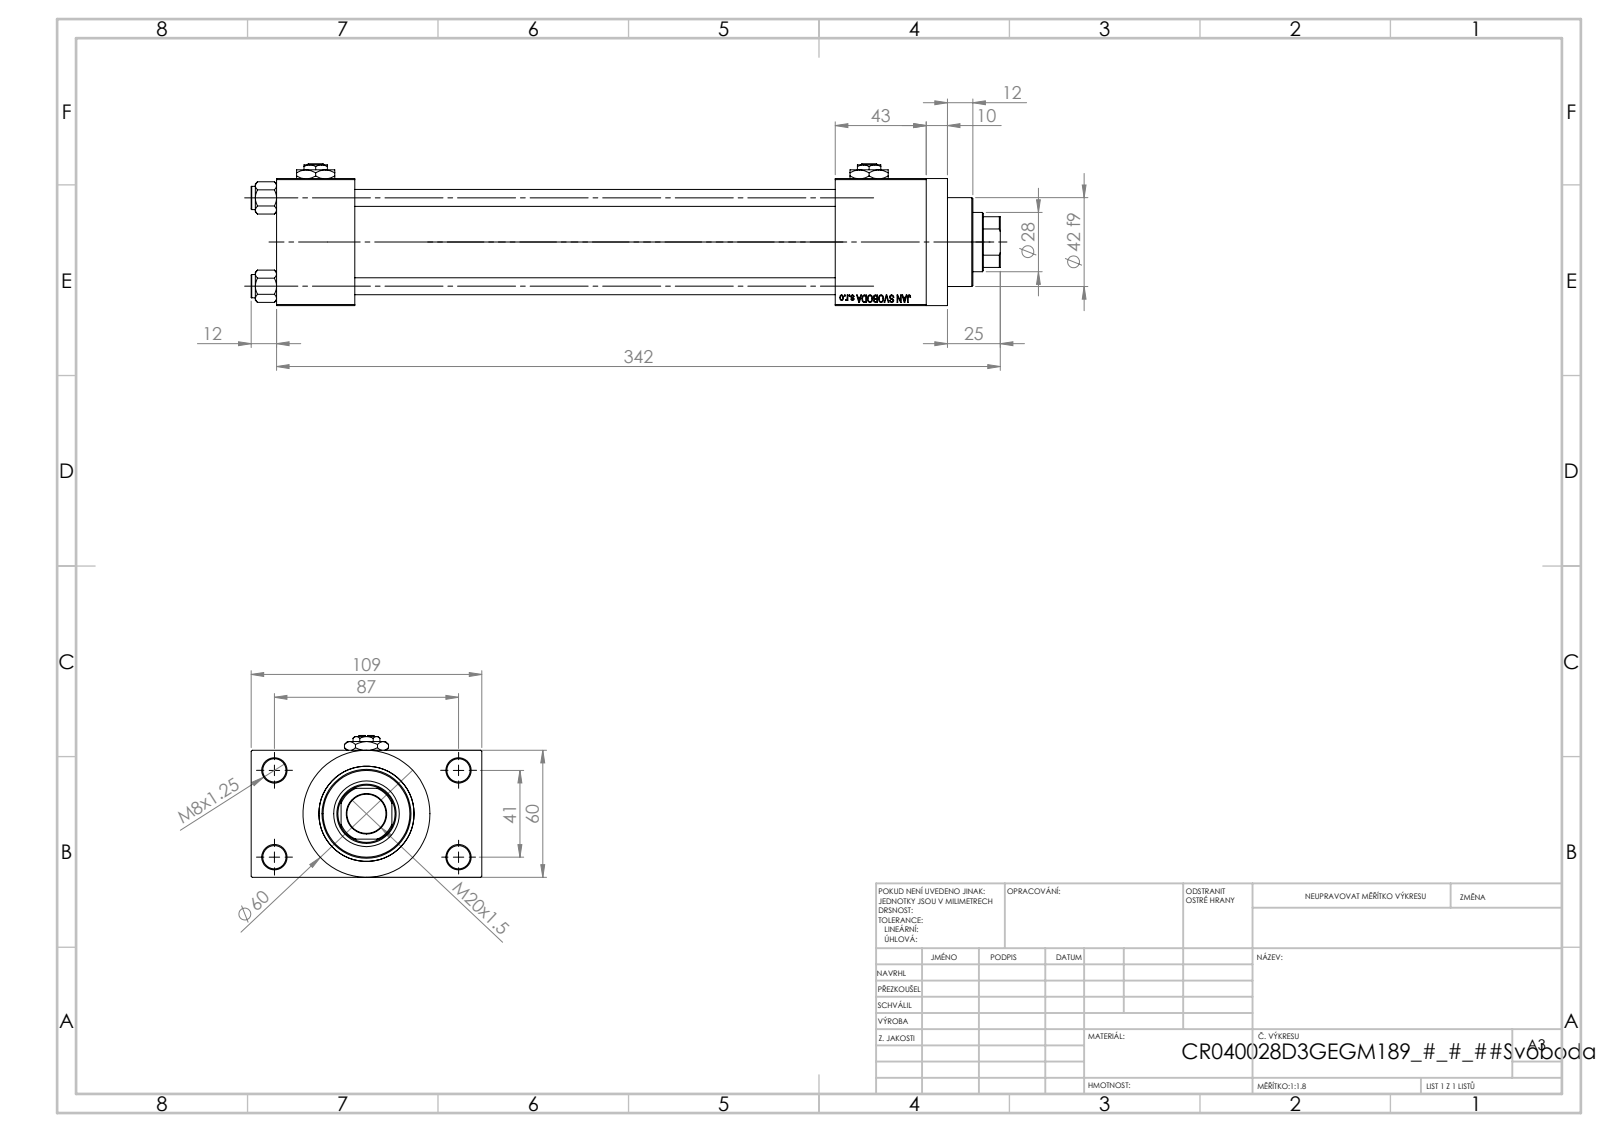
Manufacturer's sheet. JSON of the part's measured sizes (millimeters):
{"part_name": "V215CR_D_TYCINKA; V215CR_VCP_D; NUT_M5_D; V215CR_D_Body (+2 more)", "step_written_by": "SolidWorks 2019 (CONFIG_CONTROL_DESIGN)", "units": "millimeters", "bodies": {"solids": 13, "faces": 1206, "planar": 546, "cylindrical": 100, "other": 560}, "overall_size": [354, 109, 67], "volume_mm3": 738478, "surface_area_mm2": 207990, "round_holes": [[8, 4], [11, 4], [7, 2], [16.66, 2], [24, 2], [18.5, 1], [28, 1], [31, 1], [40, 1], [45, 1]], "round_bosses_or_shafts": [[11, 4], [60, 1], [46, 1], [42, 1]], "partial_cylinders_radius": [[13.5, 1]], "face_to_face_distances": [60, 24.5, 84.5, 227, 37, 264, 307, 270, 43, 109], "hole_center_spacings": [22.65, 29.49, 41.7, 47.15, 48.09, 64.35, 76.49, 41]}
